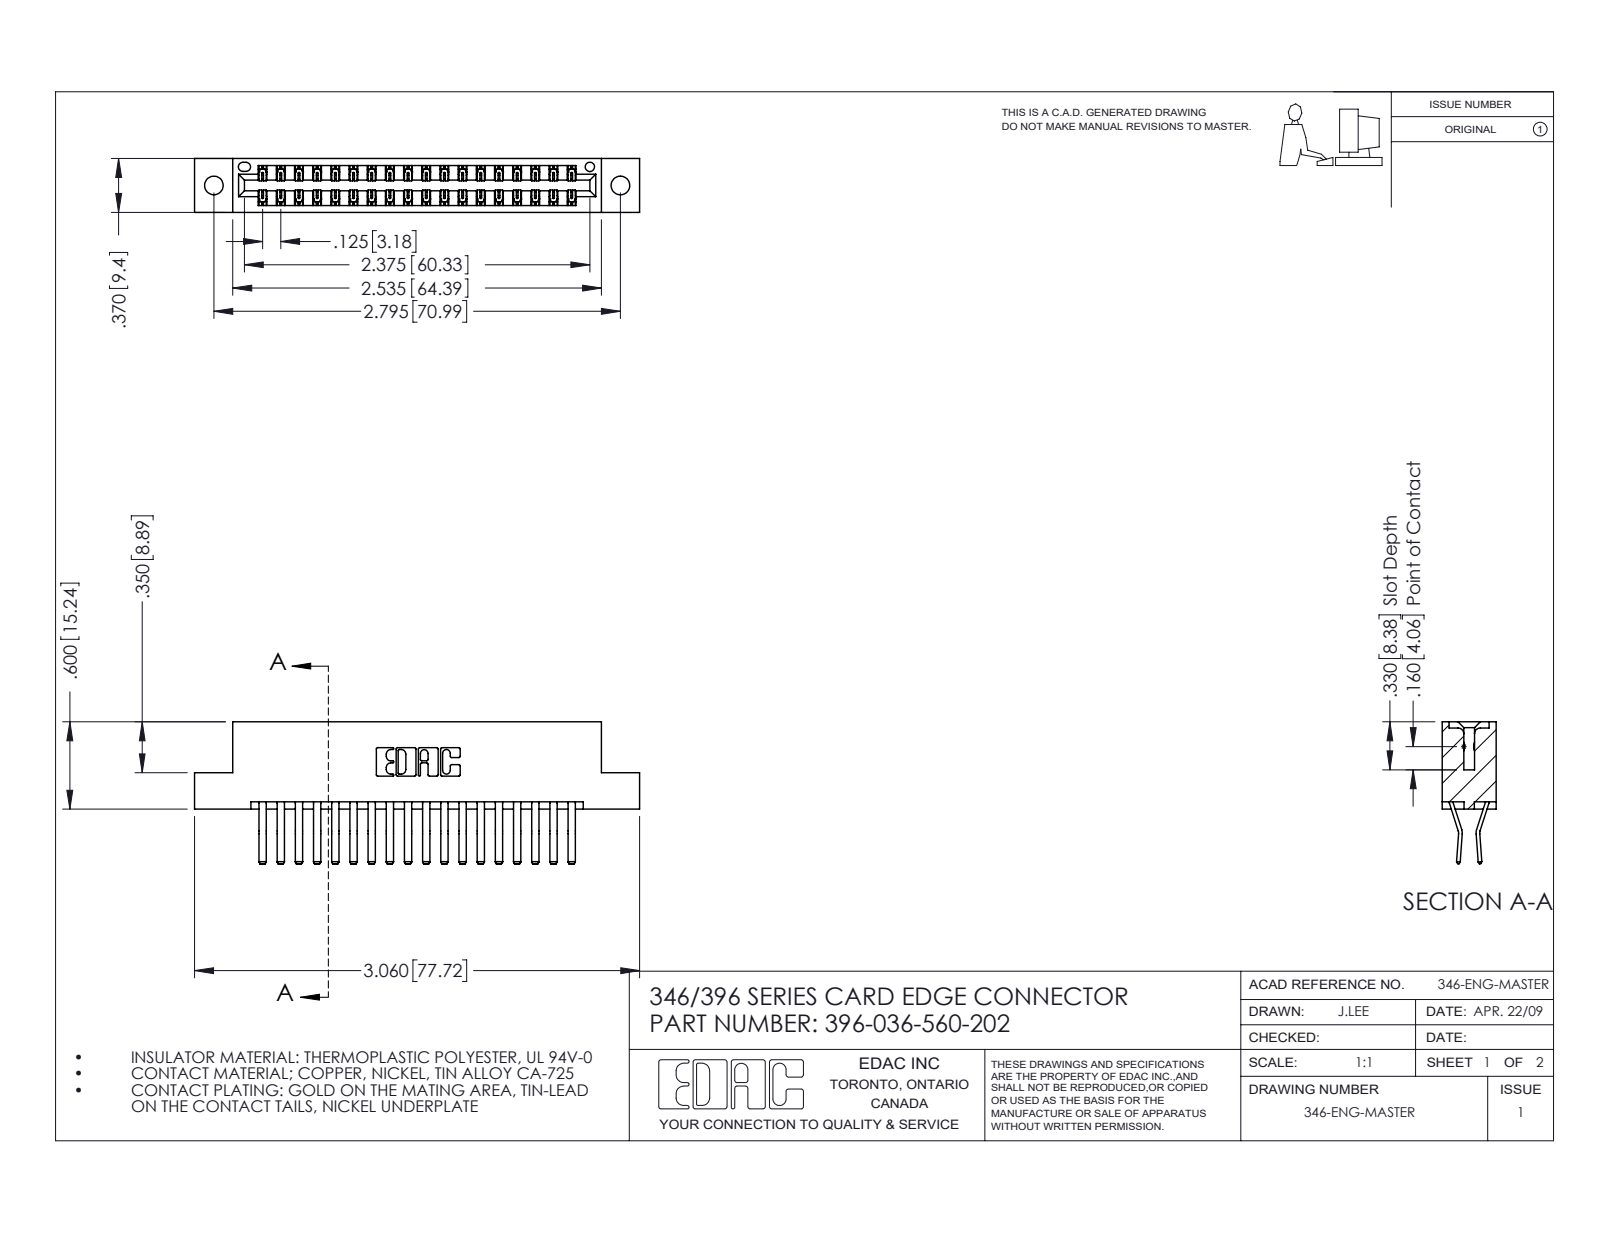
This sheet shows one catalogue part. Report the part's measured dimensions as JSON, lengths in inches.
{"part_name": "396-036-560-202; 345-292-001_560 Tail; 346 Part_Flush Mounting Lugs - 0.128 Dia", "step_written_by": "SolidWorks 2016 (CONFIG_CONTROL_DESIGN)", "units": "inches", "bodies": {"solids": 37, "faces": 2066, "planar": 1336, "cylindrical": 730, "other": 0}, "overall_size": [3.06, 0.975, 0.37], "volume_in3": 0.463, "surface_area_in2": 16.15, "round_holes": [[0.128, 2], [0.064, 1]], "partial_cylinders_radius": [[0.006, 54], [0.01, 22], [0.007, 6], [0.031, 6], [0.026, 3], [0.01, 2], [0.014, 2], [0.022, 2]], "face_to_face_distances": [0.048, 0.322, 0.25, 0.37, 0.025, 0.072, 0.298, 0.275, 0.148, 0.222], "hole_center_spacings": [0.246, 2.588, 2.795]}
